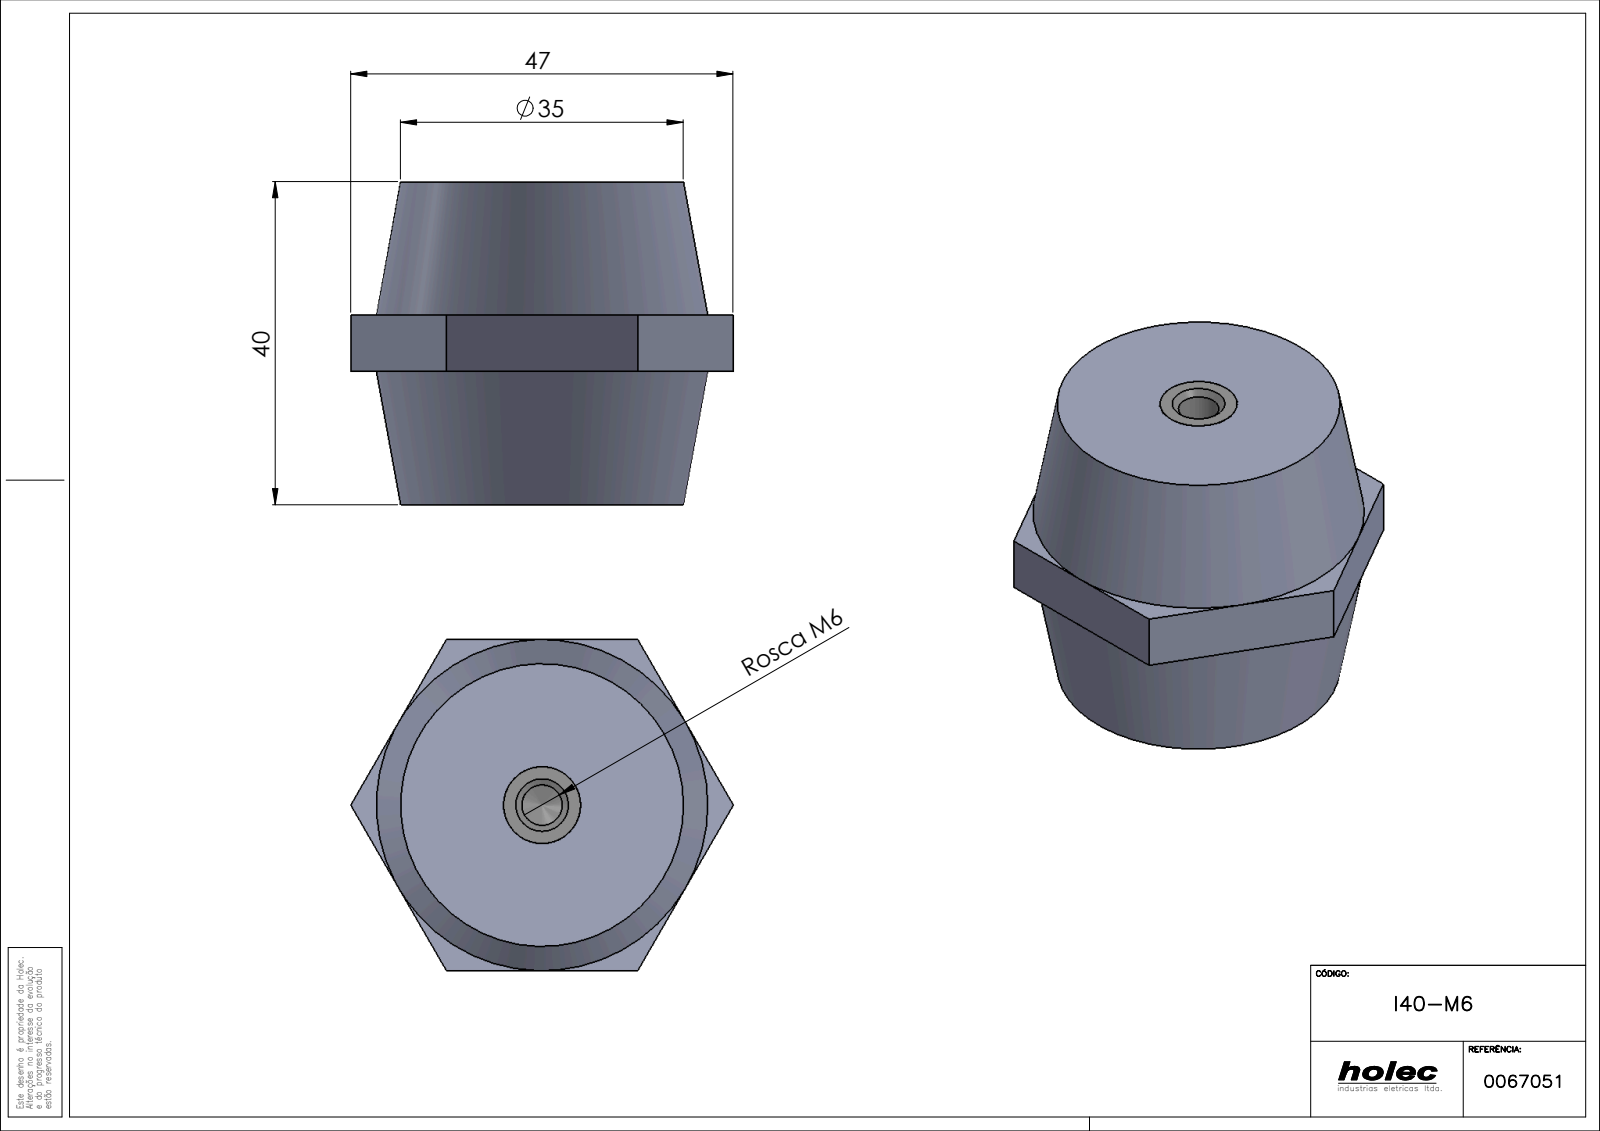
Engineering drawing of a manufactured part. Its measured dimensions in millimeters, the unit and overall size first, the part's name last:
Units: millimetres
Overall size (bounding box): 47.34 × 41 × 40
Round holes (diameter × count): ⌀5 ×1, ⌀8 ×1
Main face-to-face distances: 40, 41, 9.52, 16.5, 23.5, 32.01, 32, 2.5, 5.5, 7.99
Volume: 47 430 mm³ · Surface area: 8 864 mm²
Bodies: 3 solids, 162 faces (82 planar, 12 cylindrical, 68 other)
Part name (STEP PRODUCT): PB1_0000; PB1_0104(PB1_0104_06); I40-M6
STEP written by: SolidWorks 2017 (AUTOMOTIVE_DESIGN)
